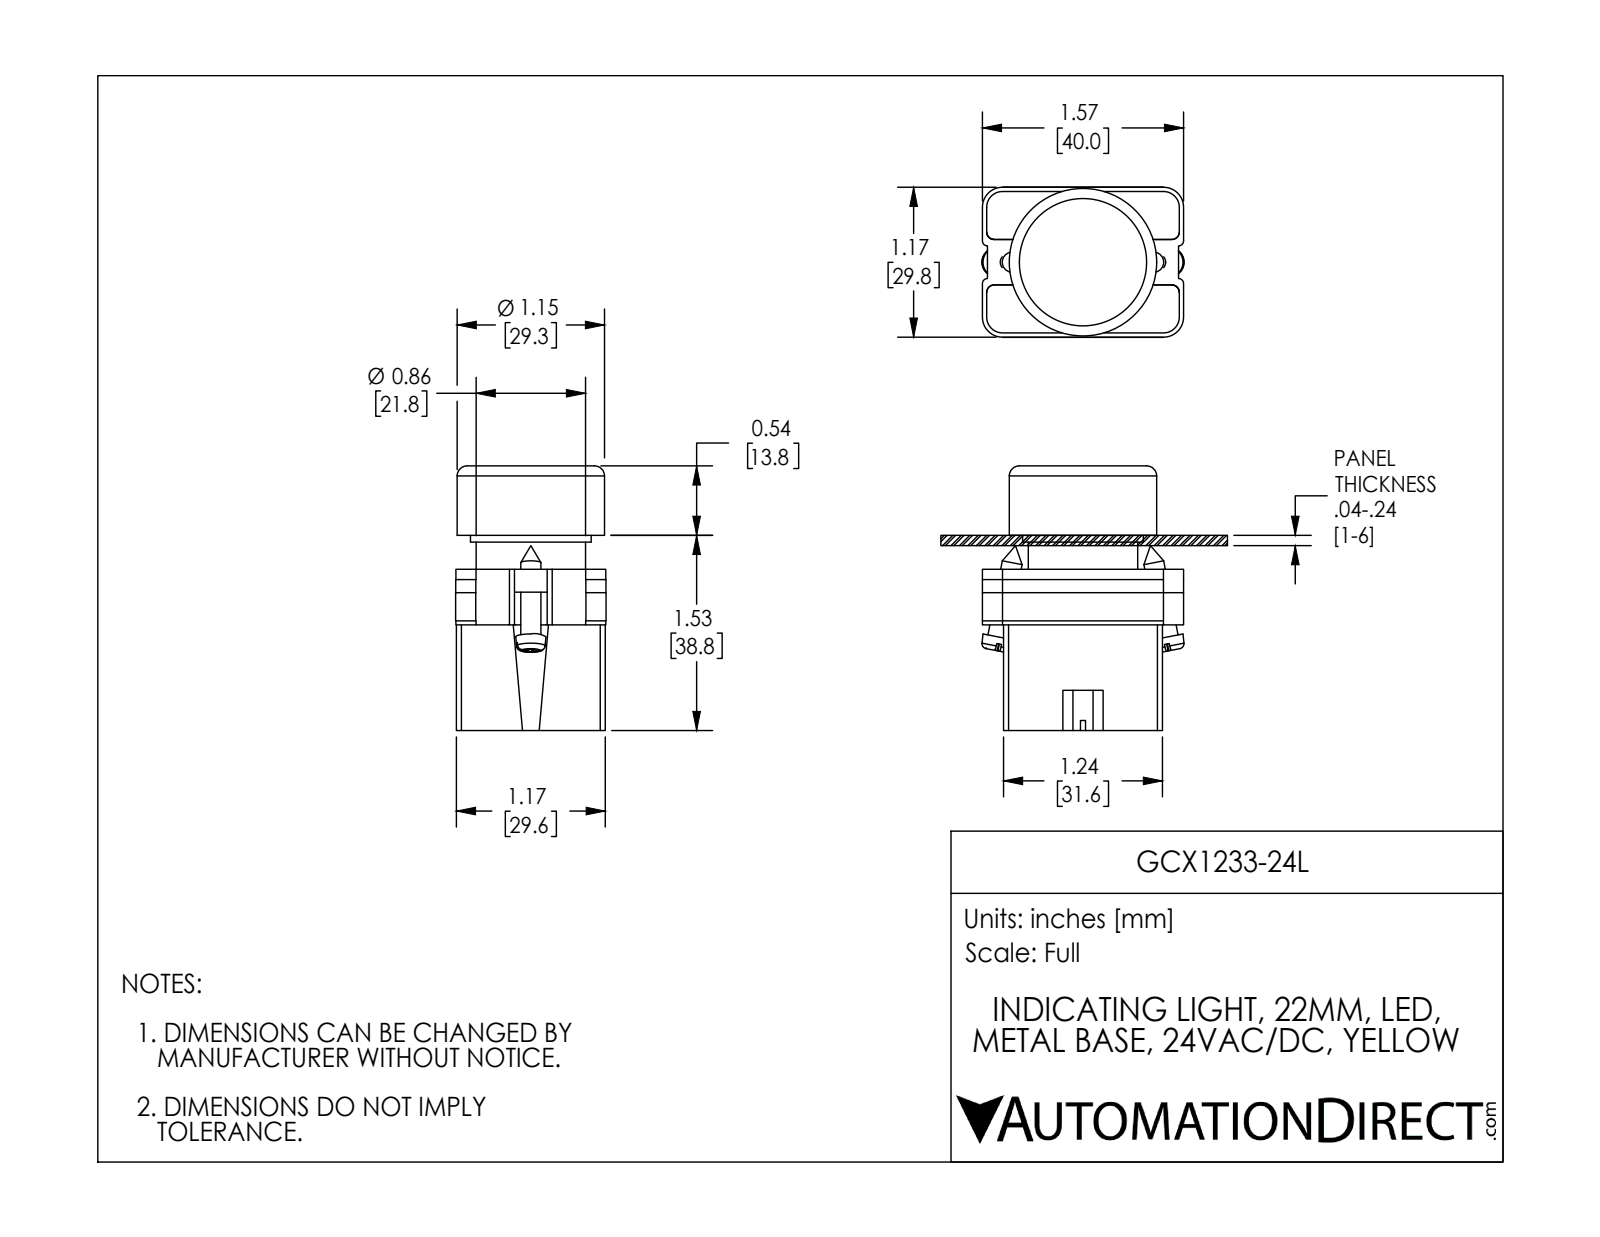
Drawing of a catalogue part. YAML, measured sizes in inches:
part_name: "ECX1050; ecx1029; GCX1233-24L; GCX1233L OPERATOR"
step_written_by: "SolidWorks 2016 (AUTOMOTIVE_DESIGN)"
units: inches
bodies: {solids: 7, faces: 339, planar: 178, cylindrical: 134, other: 27}
overall_size: [2.071, 1.581, 1.177]
volume: 2.268
surface_area: 31.19
round_holes:
  - {diameter: 0.124, count: 2}
  - {diameter: 0.13, count: 2}
  - {diameter: 0.197, count: 1}
  - {diameter: 0.469, count: 1}
  - {diameter: 0.852, count: 1}
  - {diameter: 0.878, count: 1}
  - {diameter: 0.888, count: 1}
  - {diameter: 1.102, count: 1}
round_bosses_or_shafts:
  - {diameter: 0.157, count: 4}
  - {diameter: 1.154, count: 1}
  - {diameter: 1.092, count: 1}
  - {diameter: 0.945, count: 1}
  - {diameter: 0.856, count: 1}
  - {diameter: 0.78, count: 1}
  - {diameter: 0.504, count: 1}
partial_cylinders:
  - {radius: 0.059, count: 24}
  - {radius: 0.041, count: 12}
  - {radius: 0.124, count: 12}
  - {radius: 0.157, count: 12}
  - {radius: 0.039, count: 8}
  - {radius: 0.128, count: 2}
  - {radius: 0.392, count: 1}
  - {radius: 0.398, count: 1}
face_to_face_distances: [0.86, 1.244, 0.827, 1.687, 1.136, 0.033, 1.963, 0.276, 0.031, 1.165]
